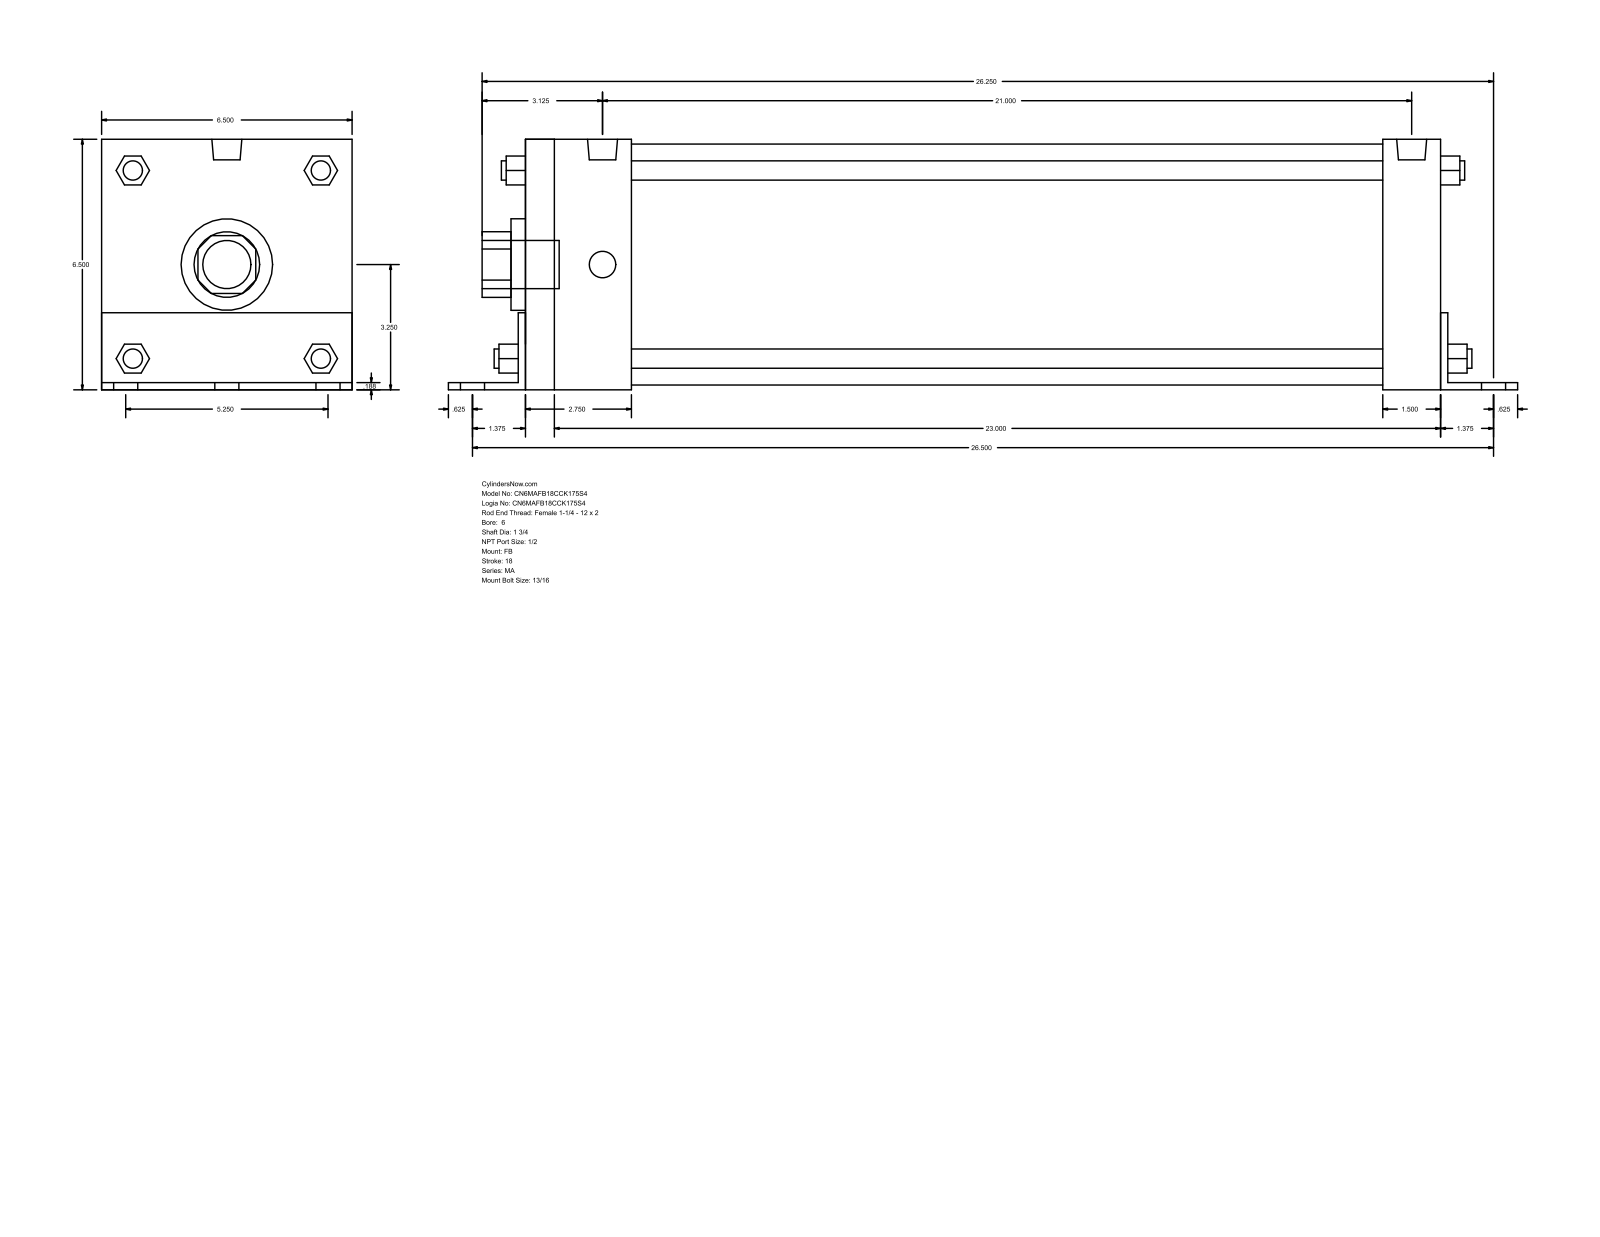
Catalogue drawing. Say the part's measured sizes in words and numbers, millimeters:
The part is named "MA_FB__0600_1.75". Its 3-D file was written by "GSSL Pune (CONFIG_CONTROL_DESIGN)". It is 0 solids with 140 faces: 105 planar, 35 cylindrical and 0 other. Overall it measures 704.85 by 165.15 by 165.1 millimeters. Round holes: 1 of diameter 44.45, 1 of diameter 60.33, 1 of diameter 158.75. Round bosses or shafts: 6 of diameter 20.64, 4 of diameter 17.46, 4 of diameter 12.7, 2 of diameter 19.77, 1 of diameter 31.75. Partial cylindrical surfaces (rounded edges, fillets, slot ends): 1 of radius 21.63, 1 of radius 32.05. The main face-to-face distances are 165.1, 4.76, 603.26, 165.15, 608.02, 4.71, 160.39, 612.78, 38.1, 42.86.
